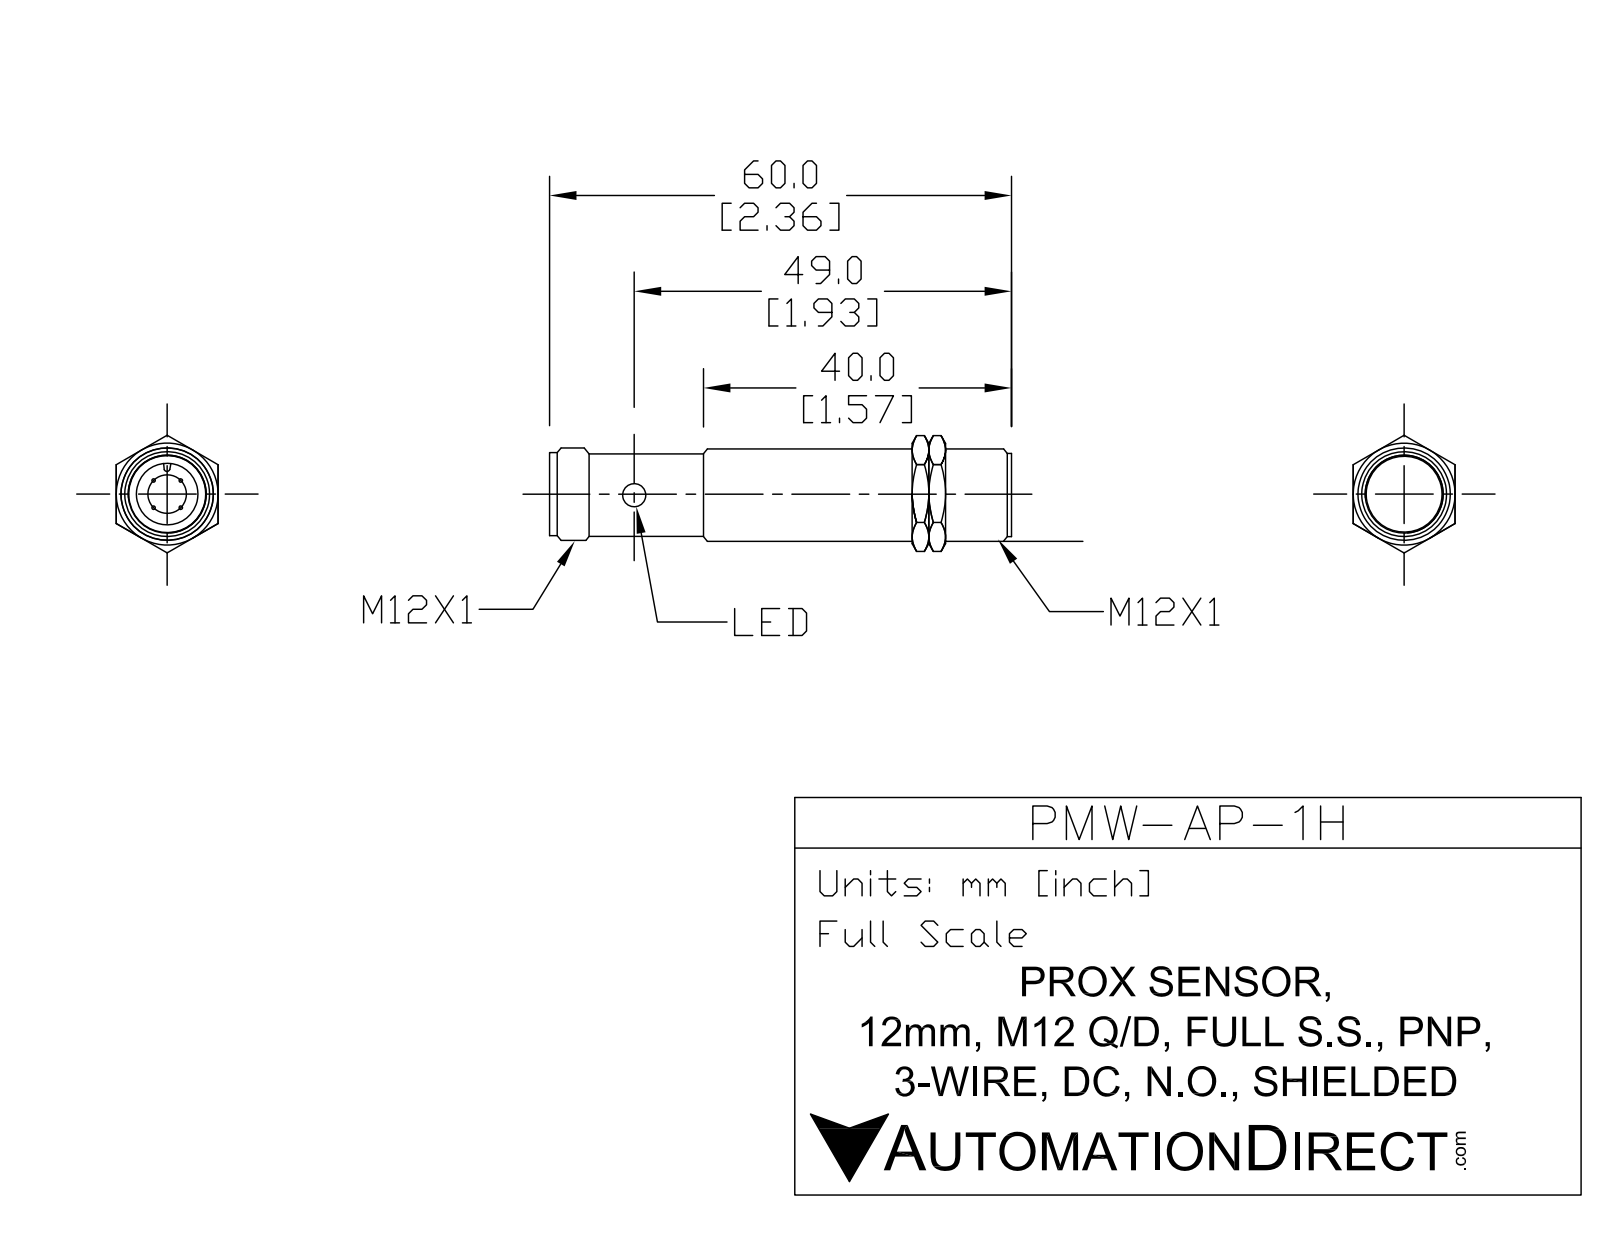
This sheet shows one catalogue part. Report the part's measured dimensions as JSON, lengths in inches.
{"part_name": "PMW-AP-1H", "step_written_by": "SolidWorks 2017 (AUTOMOTIVE_DESIGN)", "units": "inches", "bodies": {"solids": 3, "faces": 100, "planar": 26, "cylindrical": 32, "other": 42}, "overall_size": [2.362, 0.773, 0.669], "volume_in3": 0.436, "surface_area_in2": 6.196, "round_holes": [[0.098, 2], [0.331, 1], [0.43, 1]], "round_bosses_or_shafts": [[0.472, 1], [0.417, 1], [0.413, 1], [0.406, 1]], "partial_cylinders_radius": [[0.024, 1], [0.177, 1]], "face_to_face_distances": [0.157, 0.669, 0.315, 0.787, 0.63, 0.945, 1.067, 1.224, 1.382, 2.012]}
